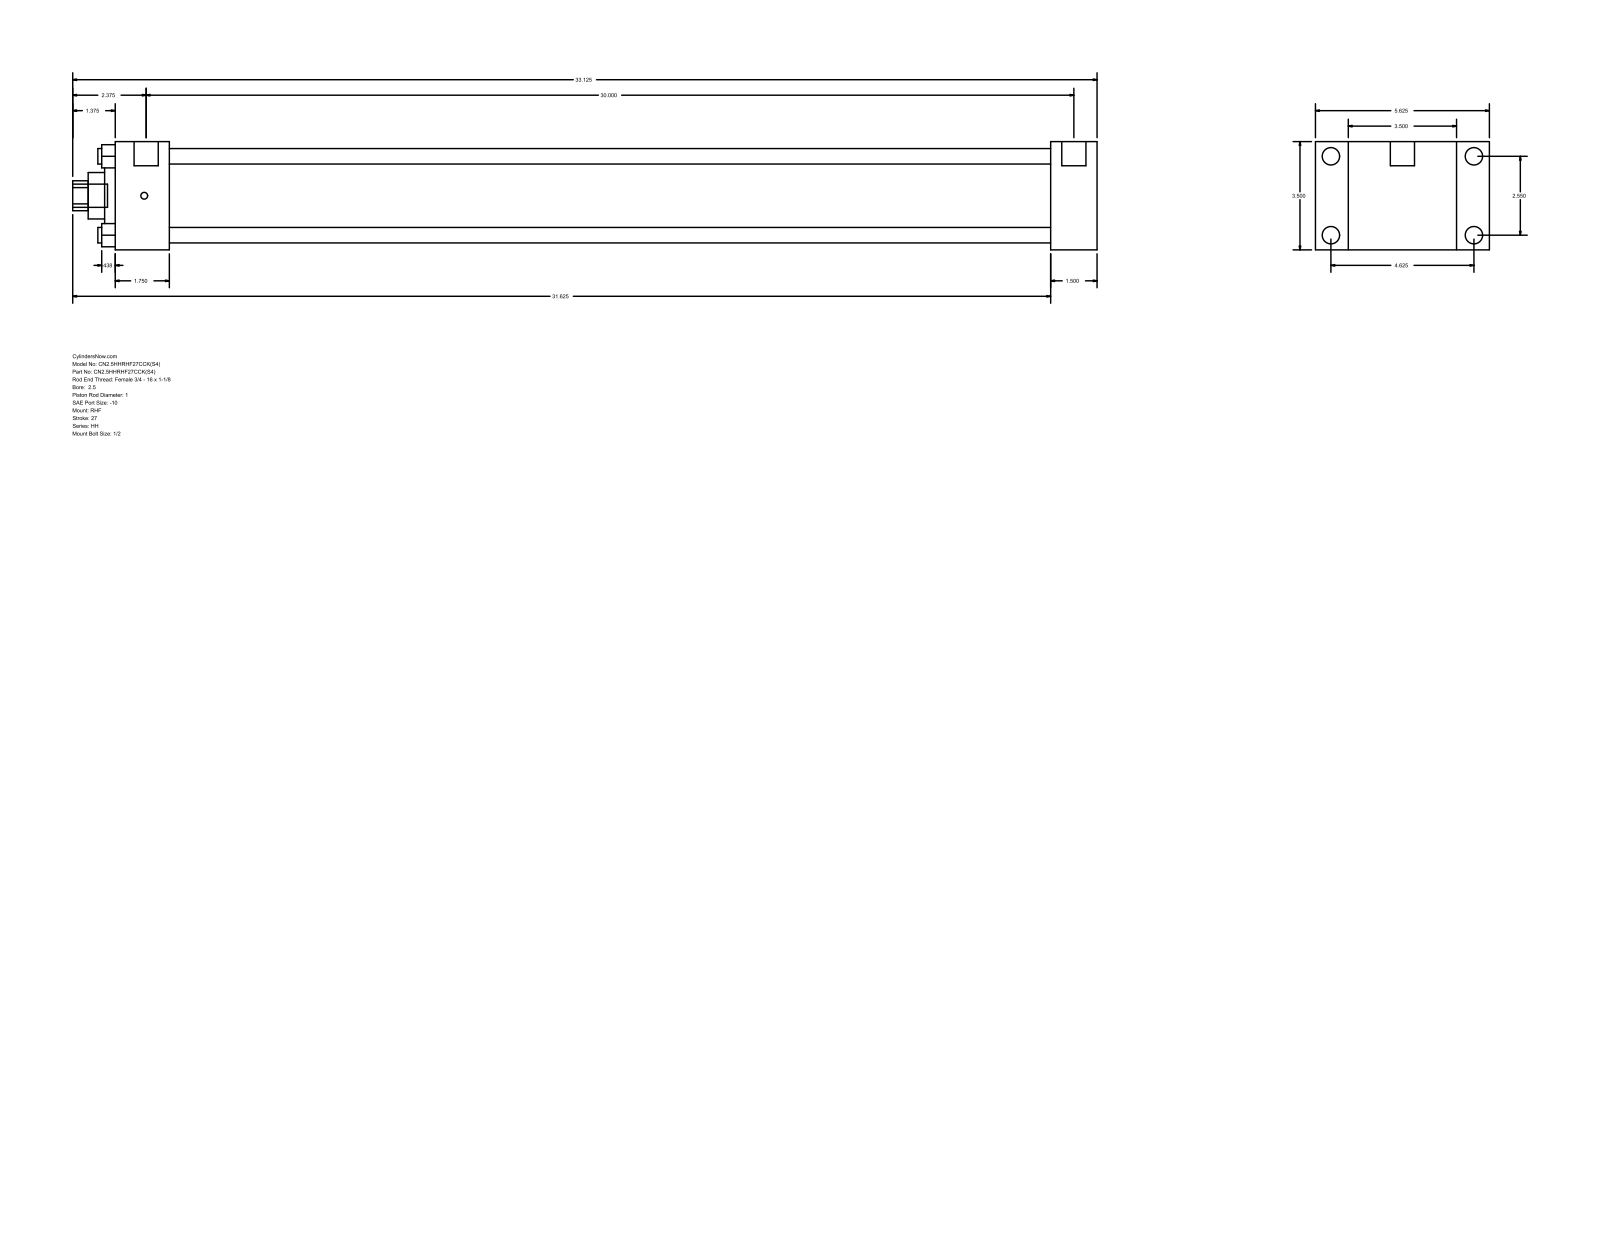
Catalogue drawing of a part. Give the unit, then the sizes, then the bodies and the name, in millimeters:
Units: millimetres
Overall size (bounding box): 841.38 × 142.88 × 88.9
Round holes (diameter × count): ⌀12.7 ×4, ⌀25.4 ×1, ⌀38.1 ×1, ⌀60.33 ×1, ⌀73.03 ×1
Round bosses / shafts (diameter × count): ⌀14.3 ×4, ⌀5.56 ×4, ⌀19.84 ×2, ⌀19.05 ×1
Partial cylindrical surfaces — rounded edges, fillets, slot ends (radius × count): R12.29 ×1
Main face-to-face distances: 88.9, 38.11, 26.99, 115.89, 768.35, 806.46, 142.88, 44.46, 723.89, 762
Hole centre spacings: 45.79, 64.76, 91.58
Bodies: 0 solids, 90 faces (61 planar, 29 cylindrical, 0 other)
Part name (STEP PRODUCT): HH_RHF__0250_1
STEP written by: GSSL Pune (CONFIG_CONTROL_DESIGN)
